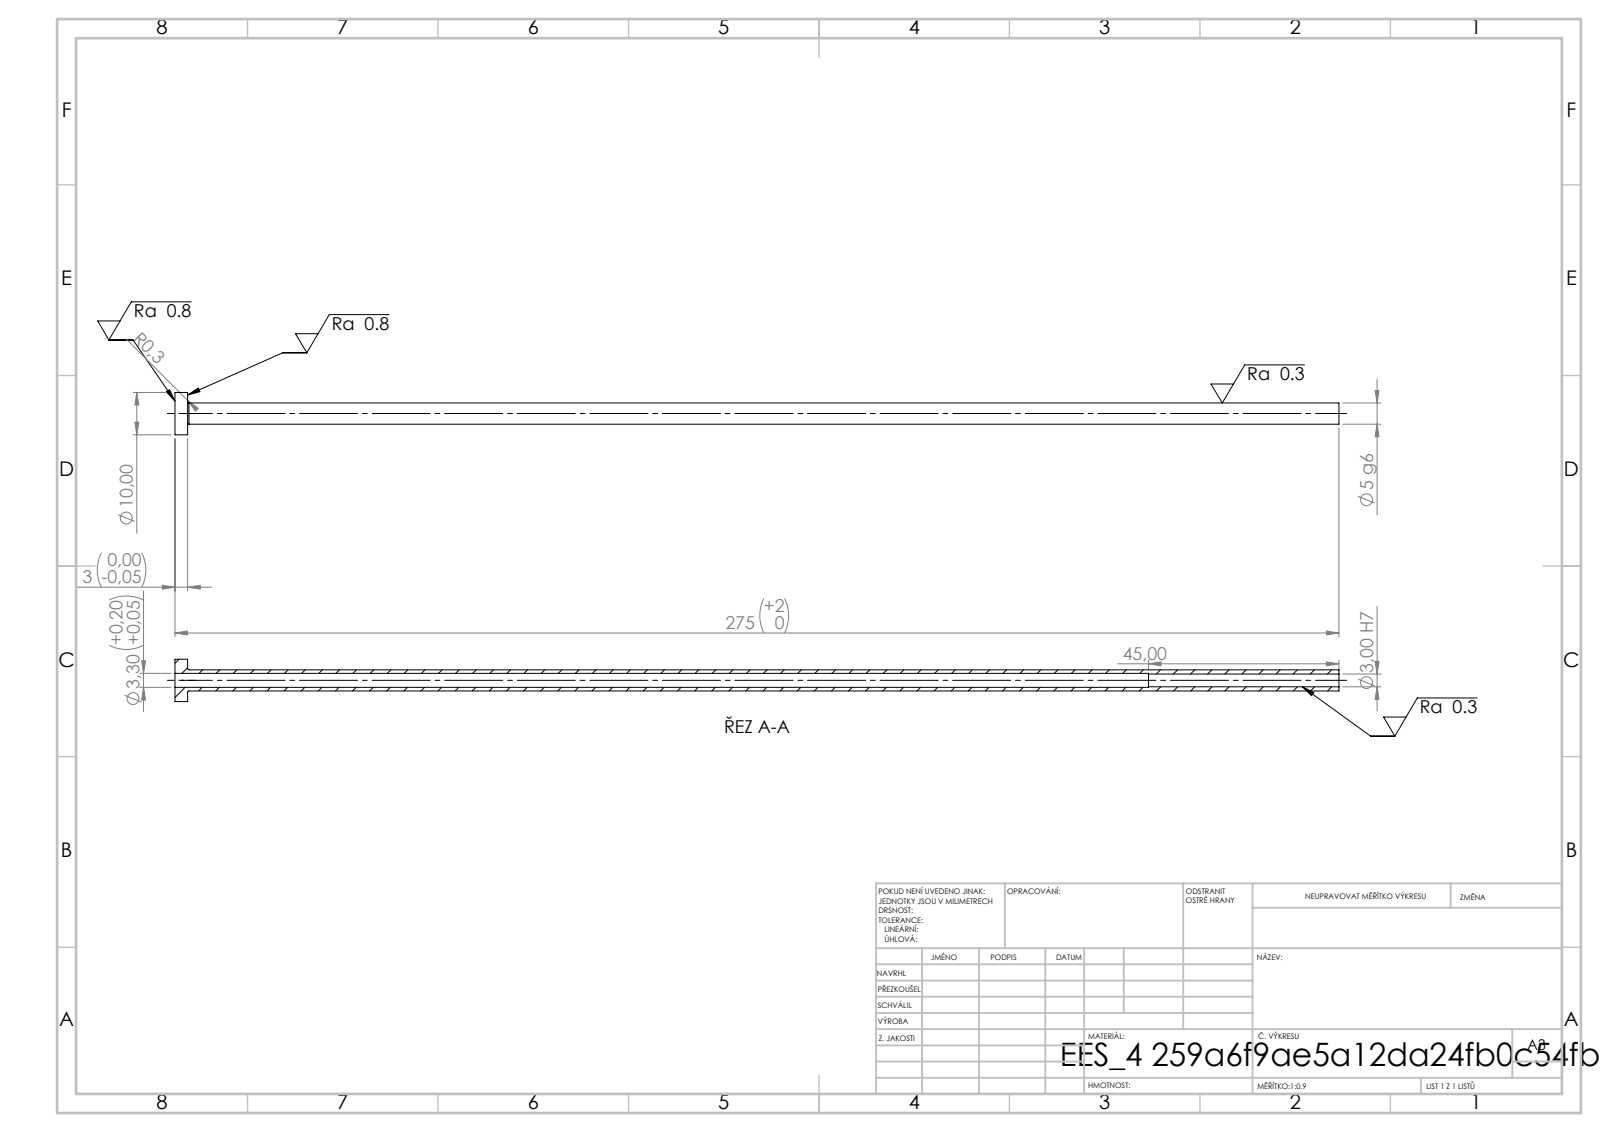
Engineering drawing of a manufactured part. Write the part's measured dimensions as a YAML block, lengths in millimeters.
step_written_by: "SolidWorks 2019 (CONFIG_CONTROL_DESIGN)"
units: millimeters
bodies: {solids: 1, faces: 14, planar: 4, cylindrical: 8, other: 2}
overall_size: [275, 10, 10]
volume: 3291
surface_area: 7316
round_holes:
  - {diameter: 3, count: 1}
  - {diameter: 3.3, count: 1}
round_bosses_or_shafts:
  - {diameter: 10, count: 1}
  - {diameter: 5, count: 1}
face_to_face_distances: [3, 275, 272, 230, 227, 45]
